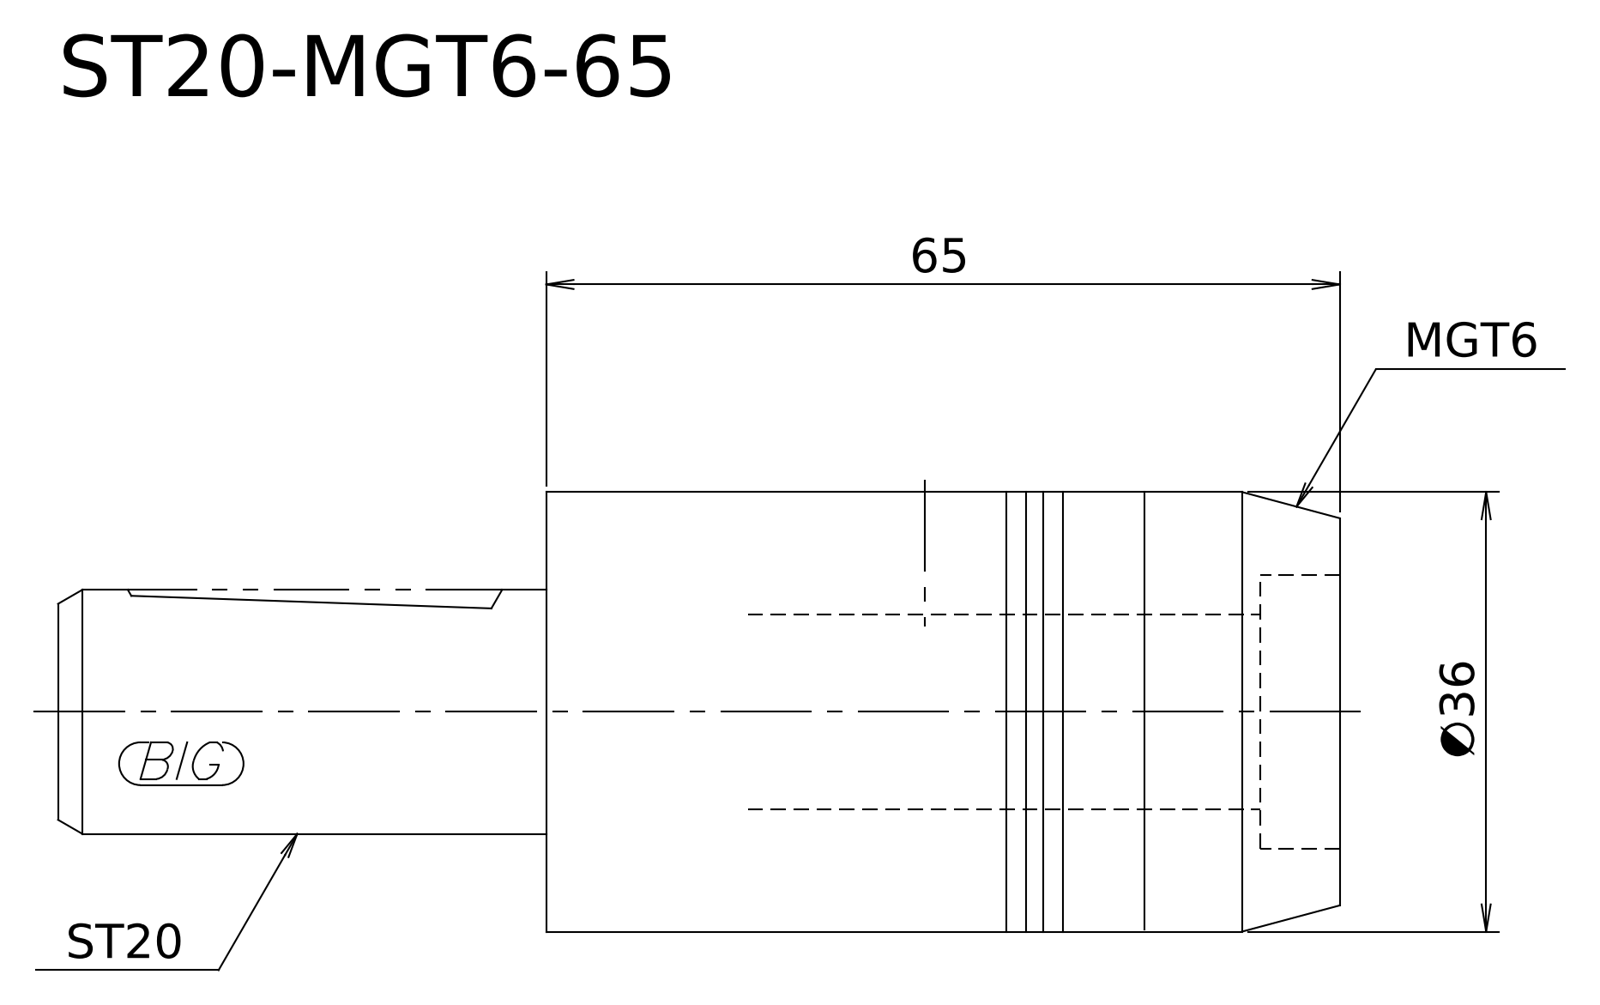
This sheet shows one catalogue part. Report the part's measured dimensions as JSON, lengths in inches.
{"step_written_by": "Kubotek KeyCreator V8.5.1 (14335) (CONFIG_CONTROL_DESIGN)", "units": "inches", "bodies": {"solids": 1, "faces": 6, "planar": 3, "cylindrical": 2, "other": 1}, "overall_size": [4.134, 1.417, 1.417], "volume_in3": 4.747, "surface_area_in2": 18.05, "round_bosses_or_shafts": [[1.417, 1], [0.787, 1]], "face_to_face_distances": [2.559, 4.134, 1.575]}
